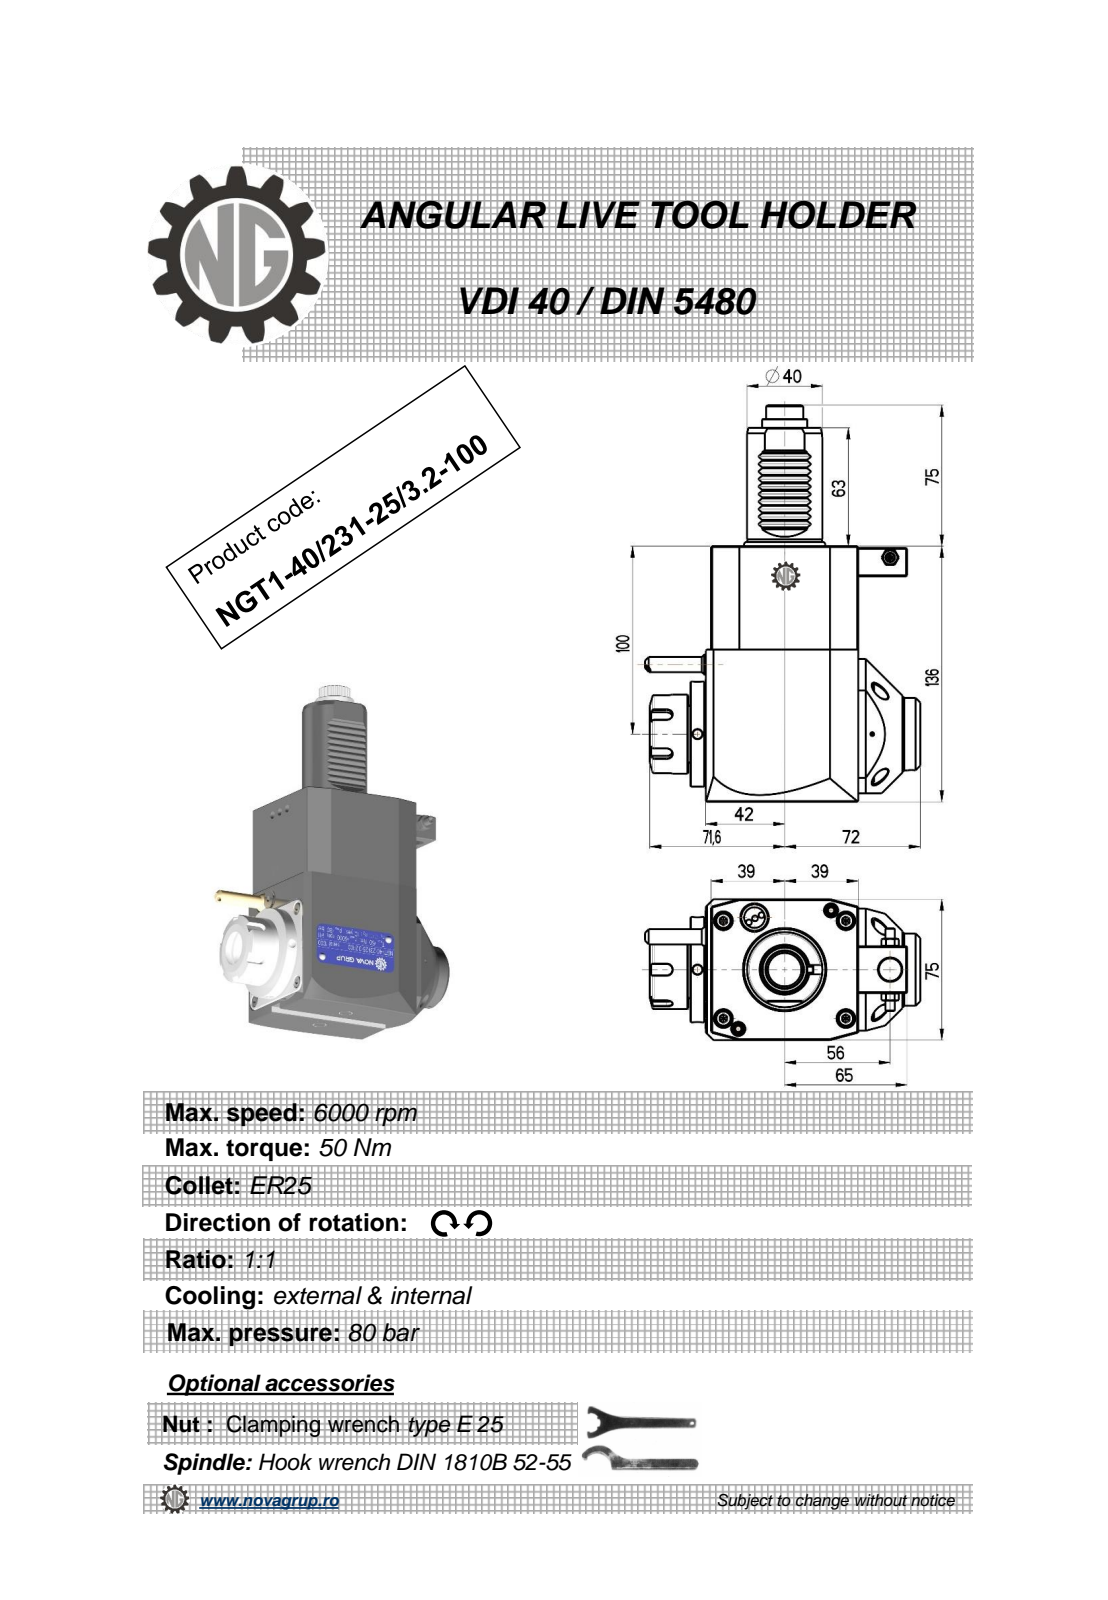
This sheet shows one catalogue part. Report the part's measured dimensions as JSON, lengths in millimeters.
{"part_name": "NGT1_40_231_25_3_2_100", "step_written_by": "PRO/ENGINEER BY PARAMETRIC TECHNOLOGY CORPORATION, 2010280 (CONFIG_CONTROL_DESIGN)", "units": "millimeters", "bodies": {"solids": 1, "faces": 549, "planar": 193, "cylindrical": 183, "other": 173}, "overall_size": [211, 146.14, 75], "volume_mm3": 1012000, "surface_area_mm2": 78017, "round_holes": [[5, 3], [3, 1], [4.2, 1], [9.5, 1], [12, 1], [20.3, 1]], "round_bosses_or_shafts": [[56, 1], [43, 1], [42, 1], [40, 1], [38.5, 1], [33, 1], [24, 1], [11.2, 1]], "partial_cylinders_radius": [[2.08, 48], [0.26, 12], [0.3, 10], [0.22, 6], [3, 5], [9.08, 1], [9.92, 1], [15, 1]], "face_to_face_distances": [75, 136, 78, 81, 3, 11, 8, 84.88, 7.5, 2.8], "hole_center_spacings": [40.93, 57.24, 91.5, 102.25, 138.89]}
